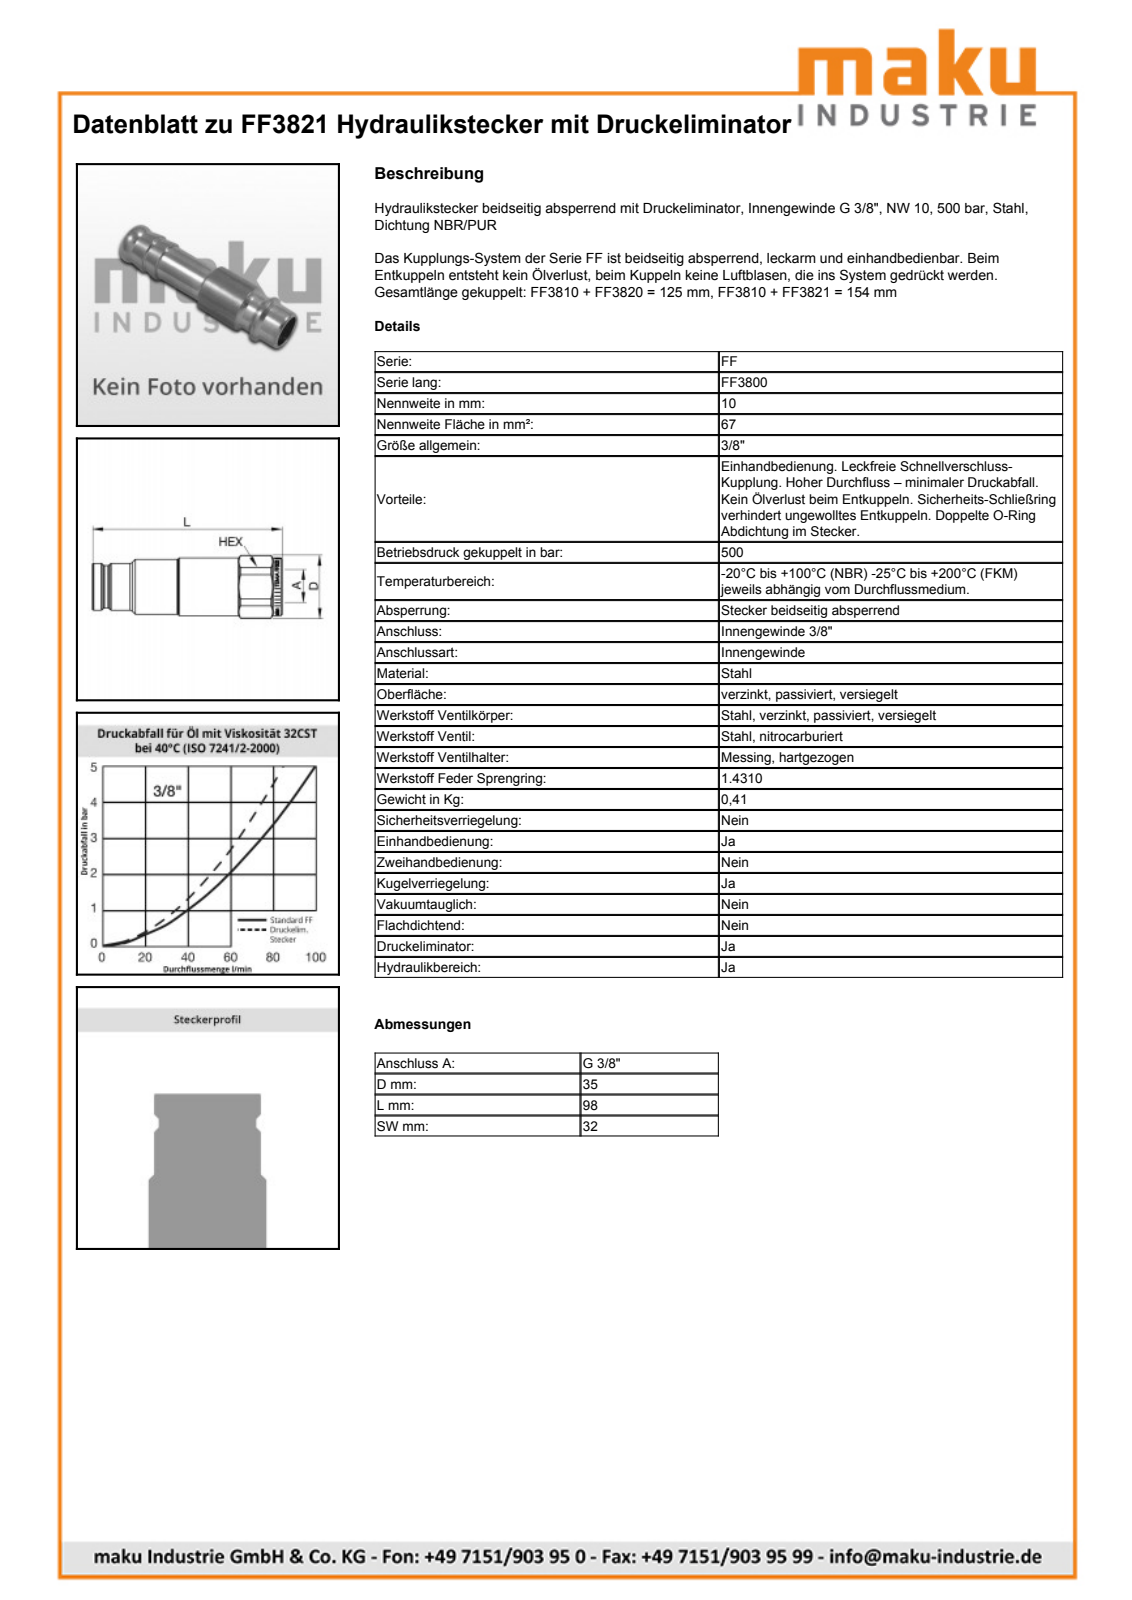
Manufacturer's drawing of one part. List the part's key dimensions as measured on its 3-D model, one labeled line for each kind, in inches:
Part name (STEP PRODUCT): FF3821
STEP written by: SolidWorks 2009 (AUTOMOTIVE_DESIGN)
Units: inches
Bodies: 1 solid, 85 faces (13 planar, 24 cylindrical, 48 other)
Overall size (bounding box): 3.862 × 1.378 × 1.26
Volume: 4.252 in³ · Surface area: 18.97 in²
Round holes (diameter × count): ⌀0.589 ×1, ⌀1.071 ×1
Round bosses / shafts (diameter × count): ⌀1.26 ×1, ⌀1.181 ×1, ⌀1.063 ×1, ⌀1.043 ×1, ⌀0.937 ×1
Partial cylindrical surfaces — rounded edges, fillets, slot ends (radius × count): R0.689 ×1
Main face-to-face distances: 1.26, 3.862, 0.548, 3.315, 3.859, 3.312, 2.35, 1.803, 1.509, 1.512
